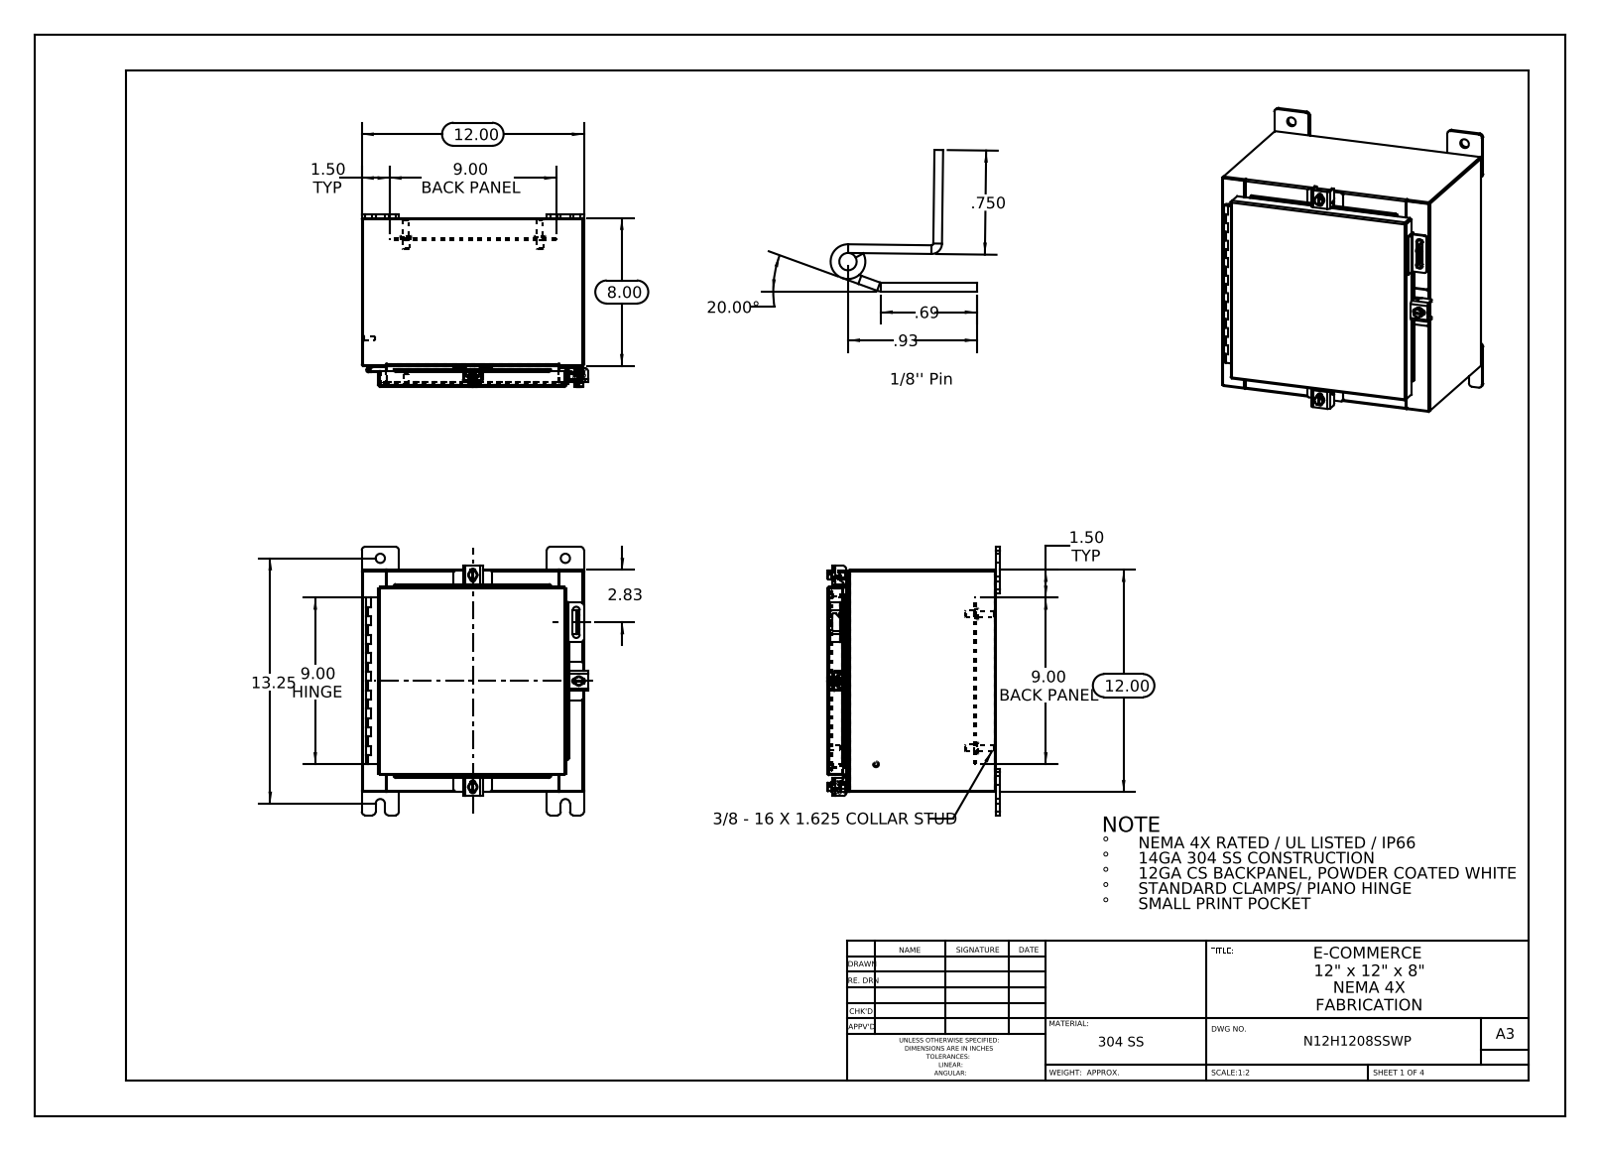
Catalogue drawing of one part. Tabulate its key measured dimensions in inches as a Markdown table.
| quantity | value |
| --- | --- |
| part name | N12H1208SSWP; Clamp Top_RTP31; N12H1208SSWP Mounting Feet; N12H1208SSWP Hinge Enclosure Side2 (+8 more) |
| STEP written by | SolidWorks 2014 (CONFIG_CONTROL_DESIGN) |
| units | inches |
| bodies | 34 solids, 1080 faces (578 planar, 418 cylindrical, 84 other) |
| overall size | 14.5 × 12.211 × 9.313 |
| volume | 71.59 in³ |
| surface area | 1 832 in² |
| round holes (diameter × count) | 0.5 × 8, 0.213 × 3, 0.26 × 3, 0.125 × 2 |
| round bosses / shafts (diameter × count) | 0.625 × 4, 0.375 × 4, 0.33 × 4, 0.25 × 4, 0.5 × 3, 0.399 × 3, 0.315 × 2, 0.236 × 2 |
| partial cylindrical surfaces (radius × count) | 0.19 × 24, 0.013 × 23, 0.088 × 21, 0.06 × 18, 0.125 × 10, 0.019 × 6, 0.1 × 6, 0.12 × 6 |
| main face-to-face distances | 0.075, 11.925, 9.039, 11.85, 12, 7.925, 1.114, 8.964, 9.114, 1 |
| hole center spacings | 4.19, 10.029, 2.226, 3.3, 5.012, 5.08, 7.25, 7.25 |
